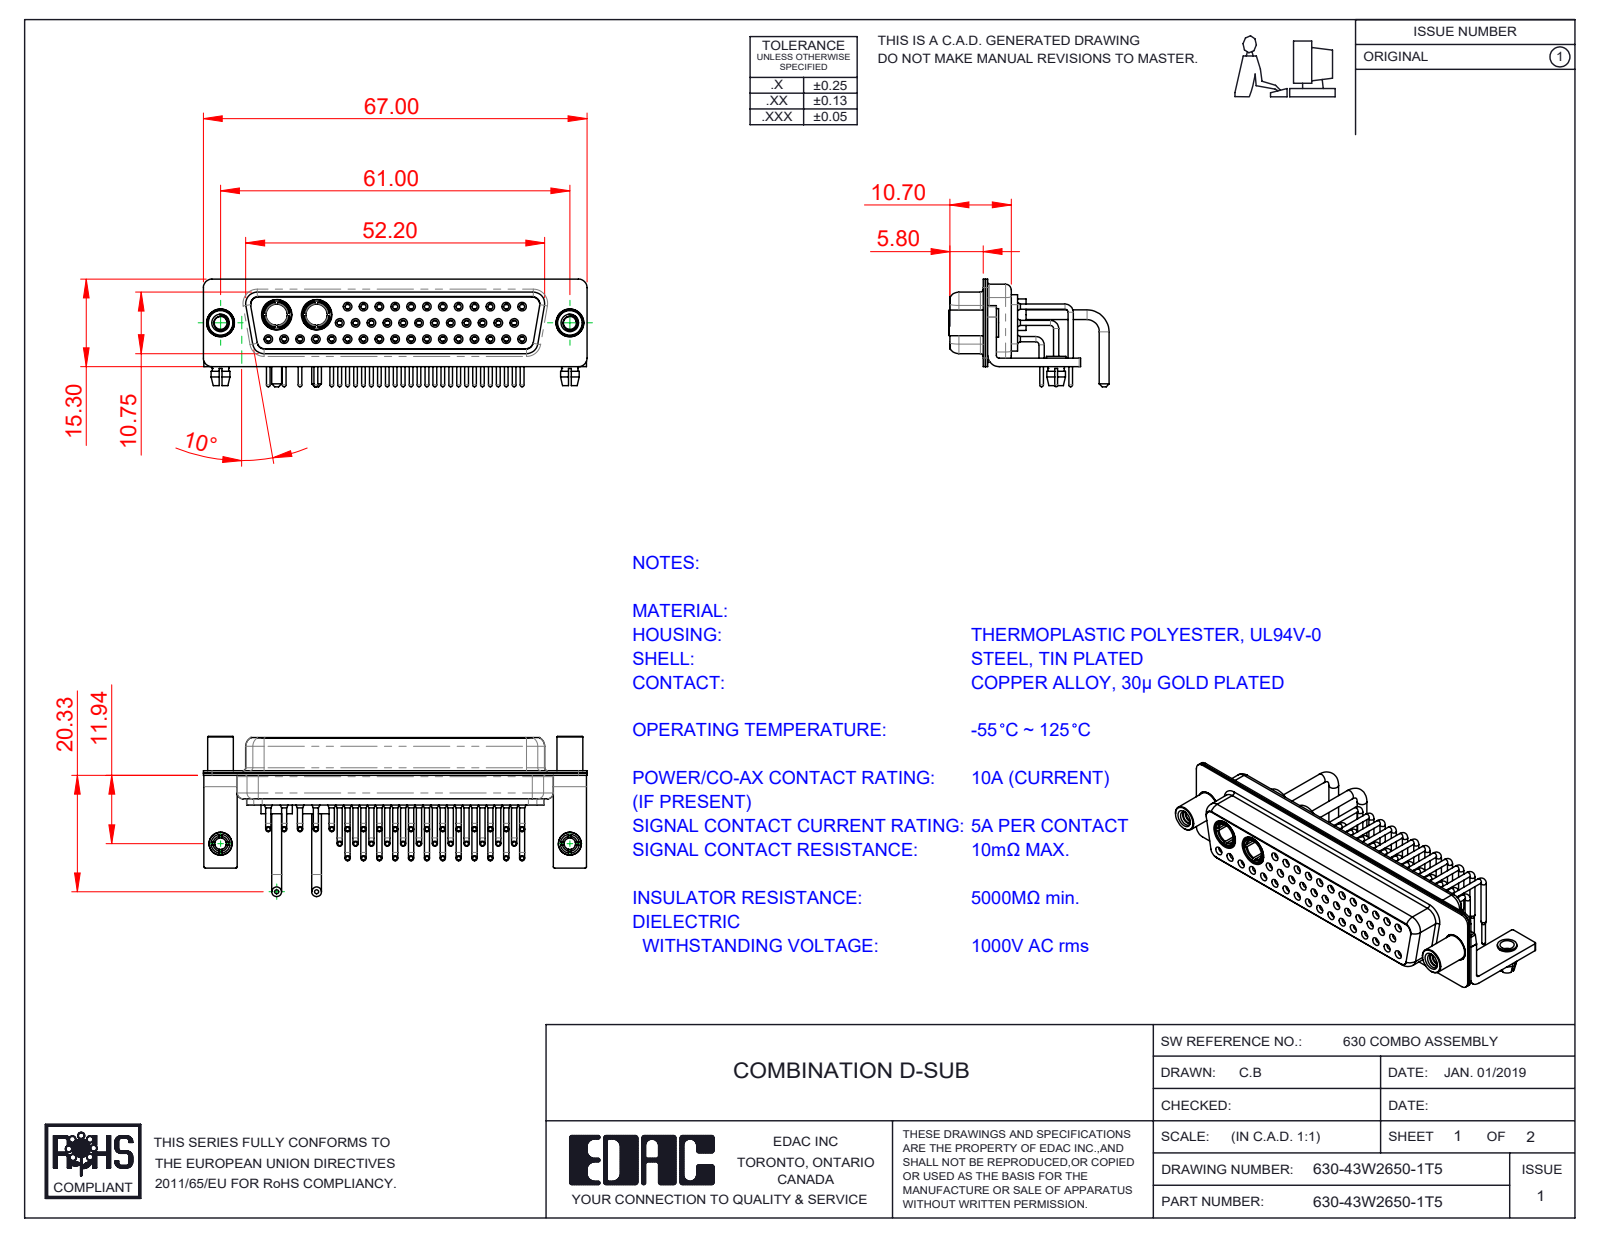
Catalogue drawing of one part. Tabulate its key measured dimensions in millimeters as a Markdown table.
| quantity | value |
| --- | --- |
| part name | 630-43W2650-1T5; 630Combo Contact Row 1_50 Contacts; 630Combo Contact Row 3; 630Combo Shell Rear_50 Contacts (+7 more) |
| STEP written by | SolidWorks 2020 (CONFIG_CONTROL_DESIGN) |
| units | millimeters |
| bodies | 54 solids, 2788 faces (810 planar, 1222 cylindrical, 756 other) |
| overall size | 67 × 27.98 × 18.8 |
| volume | 7 628 mm³ |
| surface area | 17 058 mm² |
| round holes (diameter × count) | 2 × 43, 0.9 × 41, 1.1 × 41, 1.5 × 41, 1.6 × 29, 1.7 × 12, 4.85 × 4, 2.26 × 2, 2.5 × 2, 3.2 × 2, 3.7 × 2, 4 × 2 |
| round bosses / shafts (diameter × count) | 0.9 × 41, 0.65 × 41, 1.6 × 12, 1.7 × 4, 5.5 × 2, 5.2 × 2, 5 × 2, 4.96 × 2 |
| partial cylindrical surfaces (radius × count) | 0.25 × 16, 1.5 × 16, 2 × 13, 1.35 × 12, 1.6 × 8, 0.5 × 5, 0.6 × 4, 0.65 × 4 |
| main face-to-face distances | 0.4, 1.5, 6, 5.6, 0.8, 5.2, 5.8, 11.28, 1.82, 6.2 |
| hole center spacings | 2.77, 3.16, 5.54, 8.31, 11.08, 13.85, 16.62, 19.39 |
